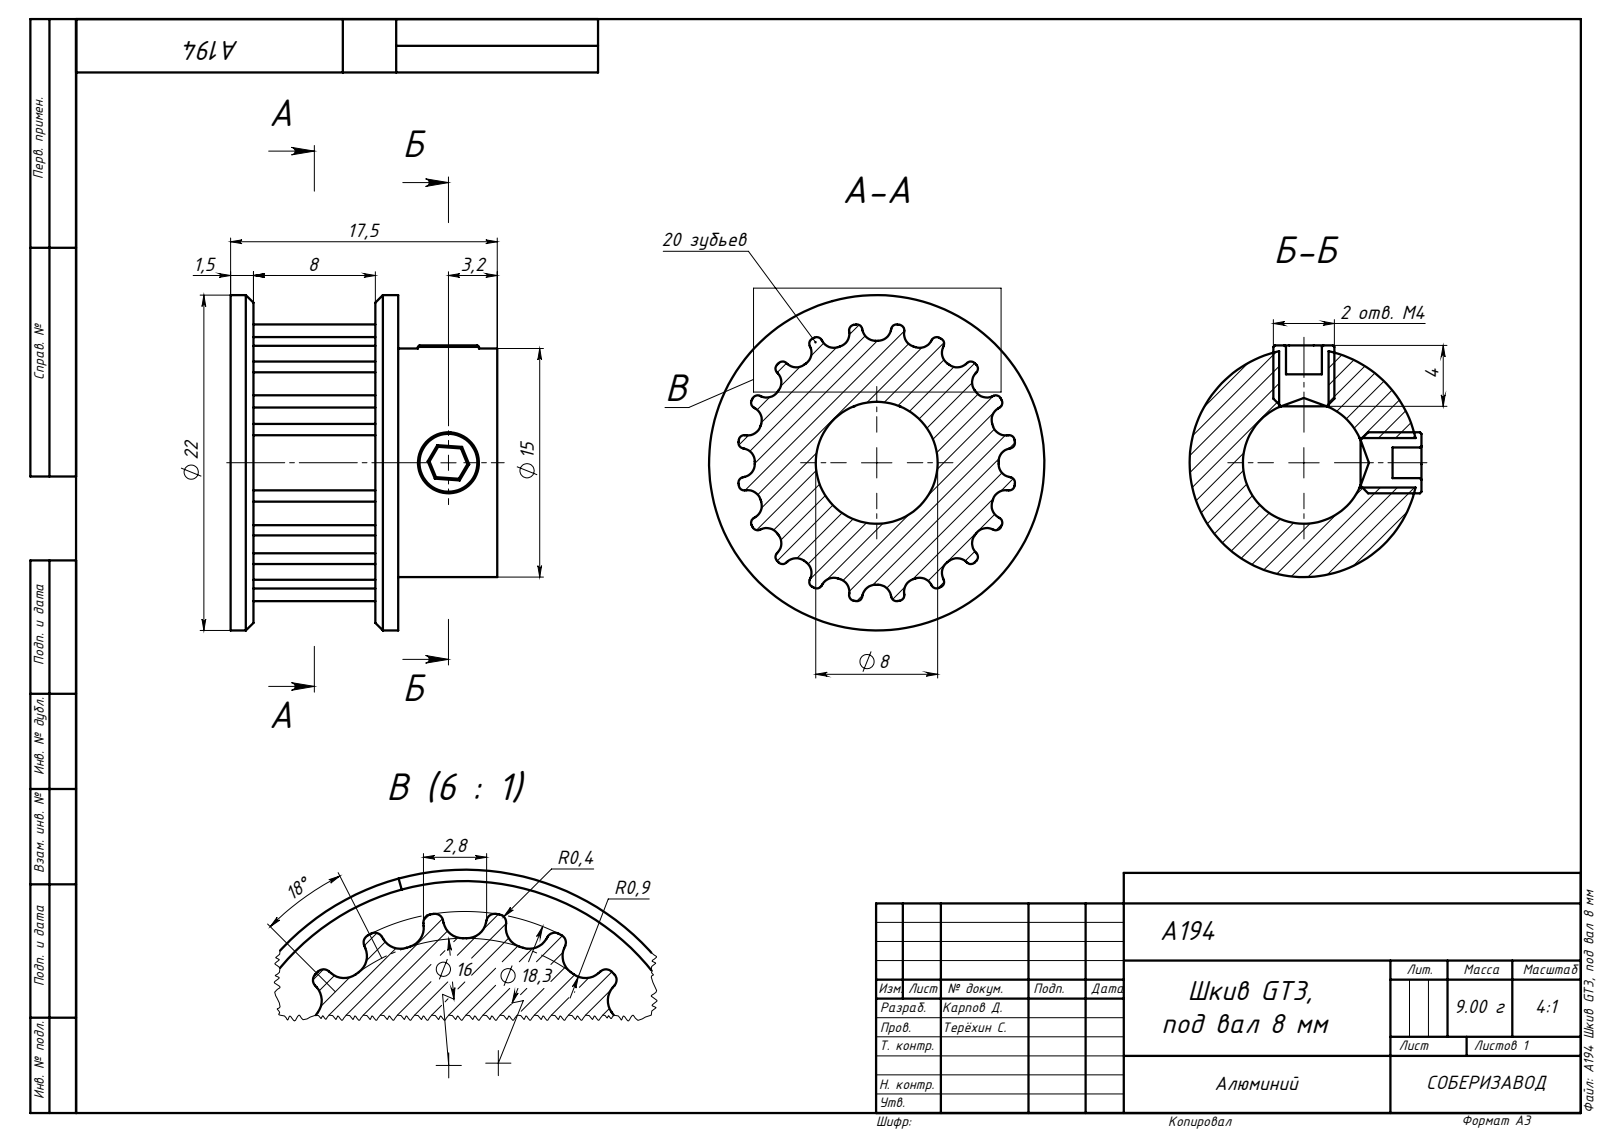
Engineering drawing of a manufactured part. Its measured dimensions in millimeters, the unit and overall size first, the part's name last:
Units: millimetres
Overall size (bounding box): 22 × 22 × 17.5
Round holes (diameter × count): ⌀3.24 ×2, ⌀8 ×1
Round bosses / shafts (diameter × count): ⌀4 ×2, ⌀22 ×1, ⌀15 ×1
Partial cylindrical surfaces — rounded edges, fillets, slot ends (radius × count): R0.36 ×40, R0.87 ×40, R9.17 ×1
Main face-to-face distances: 1.5, 9.5, 8, 11, 16, 17.5, 6.5, 1.94, 1.9, 2.24
Volume: 3 217 mm³ · Surface area: 2 726 mm²
Bodies: 3 solids, 261 faces (93 planar, 152 cylindrical, 16 other)
Part name (STEP PRODUCT): A194 Шкив GT3, под вал 8 мм; A194 Шкив GT3, под вал 8 мм_00
STEP written by: SolidWorks 2019 (AUTOMOTIVE_DESIGN)
